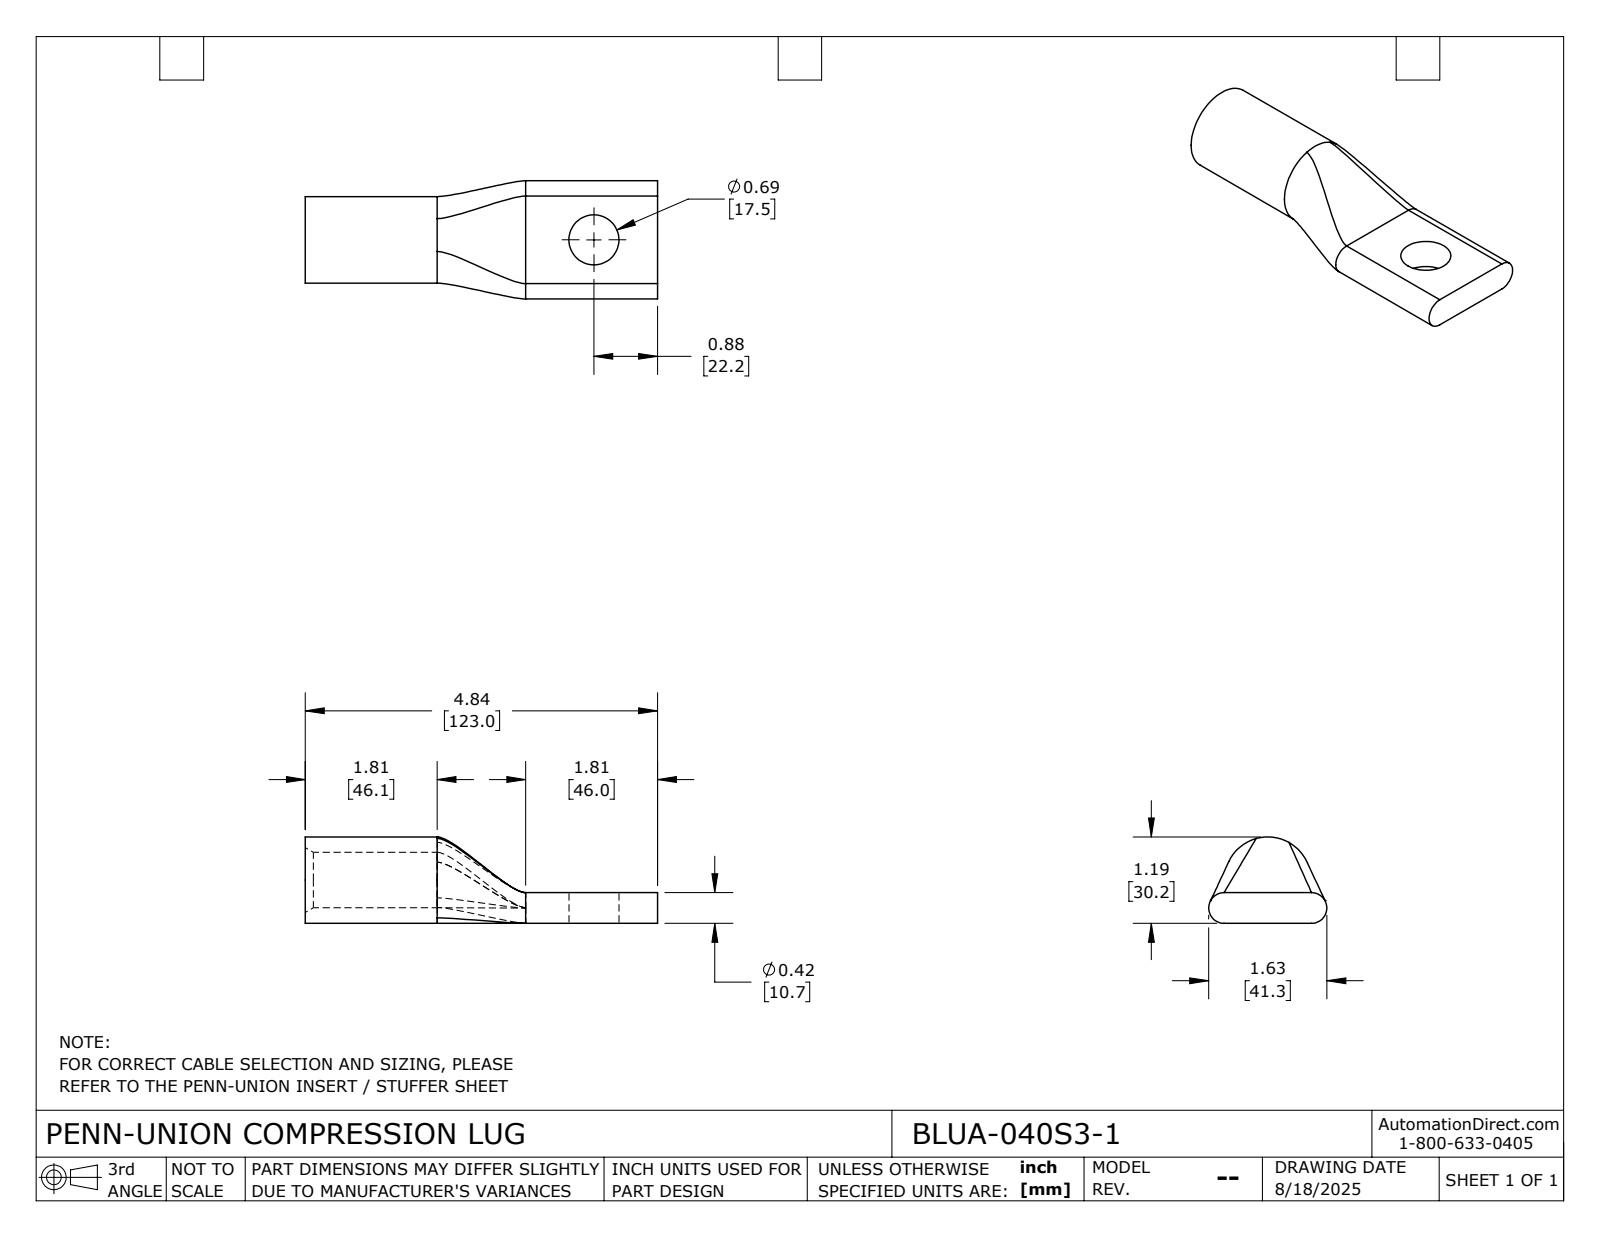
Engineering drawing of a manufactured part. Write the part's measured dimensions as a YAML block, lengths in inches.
part_name: "BLUA-040S3-1"
step_written_by: "SolidWorks 2024 (CONFIG_CONTROL_DESIGN)"
units: inches
bodies: {solids: 1, faces: 24, planar: 5, cylindrical: 9, other: 10}
overall_size: [4.844, 1.625, 1.188]
volume: 2.977
surface_area: 27.09
round_holes:
  - {diameter: 0.687, count: 1}
  - {diameter: 0.762, count: 1}
round_bosses_or_shafts:
  - {diameter: 1.188, count: 1}
partial_cylinders:
  - {radius: 0.211, count: 2}
face_to_face_distances: [0.422, 4.844, 3.031, 1.813]
